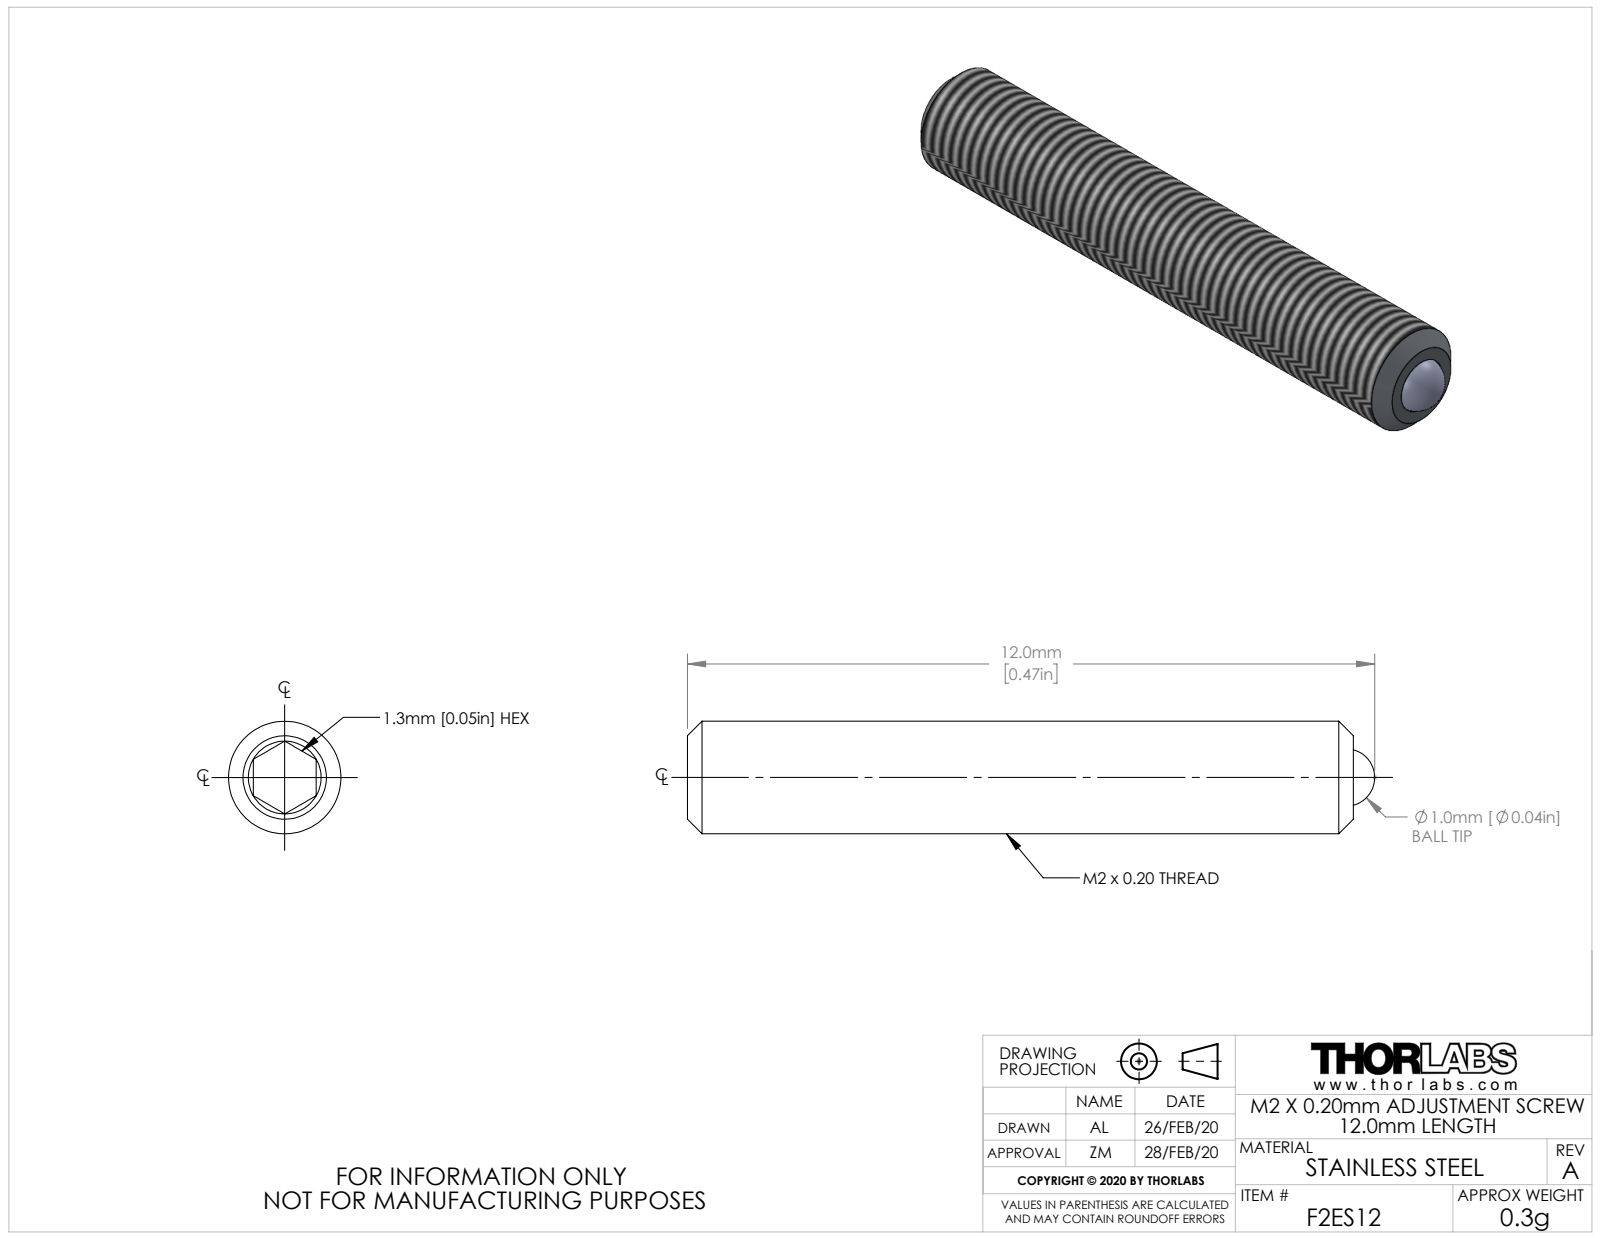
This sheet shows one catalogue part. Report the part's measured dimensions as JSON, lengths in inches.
{"part_name": "TTN210091-E0W", "step_written_by": "SolidWorks 2018 (AUTOMOTIVE_DESIGN)", "units": "inches", "bodies": {"solids": 2, "faces": 28, "planar": 9, "cylindrical": 4, "other": 15}, "overall_size": [0.472, 0.077, 0.077], "volume_in3": 0.002, "surface_area_in2": 0.136, "round_holes": [[0.039, 1]], "round_bosses_or_shafts": [[0.077, 1]], "face_to_face_distances": [0.043, 0.378, 0.08, 0.458]}
